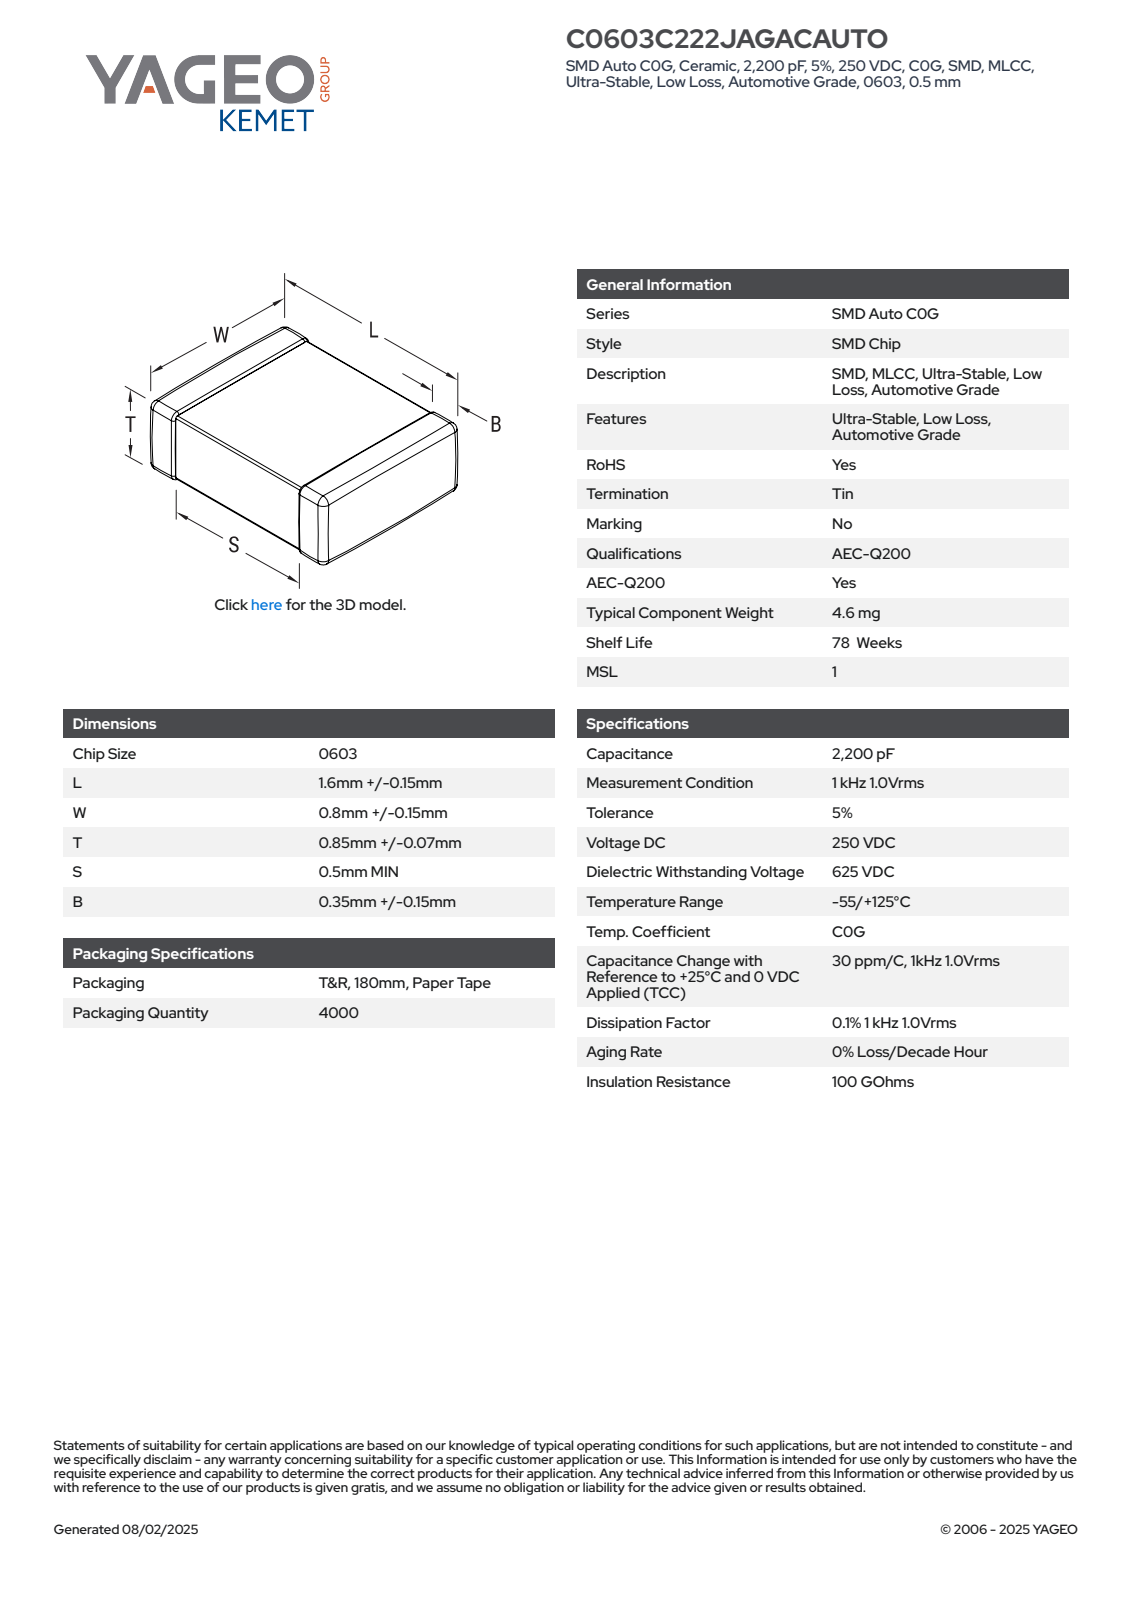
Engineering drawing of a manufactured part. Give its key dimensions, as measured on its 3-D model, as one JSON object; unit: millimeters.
{"part_name": "CCS_CCSTD_0603_L1.75W0.95T0.92B0.35", "step_written_by": "SolidWorks 2021 (AUTOMOTIVE_DESIGN)", "units": "millimeters", "bodies": {"solids": 4, "faces": 125, "planar": 71, "cylindrical": 38, "other": 16}, "overall_size": [1.75, 0.95, 0.92], "volume_mm3": 1, "surface_area_mm2": 8, "face_to_face_distances": [0.9, 0.93, 0.92, 0.95, 1.75, 0.91, 0.88, 0.89, 0.81, 0.94]}
